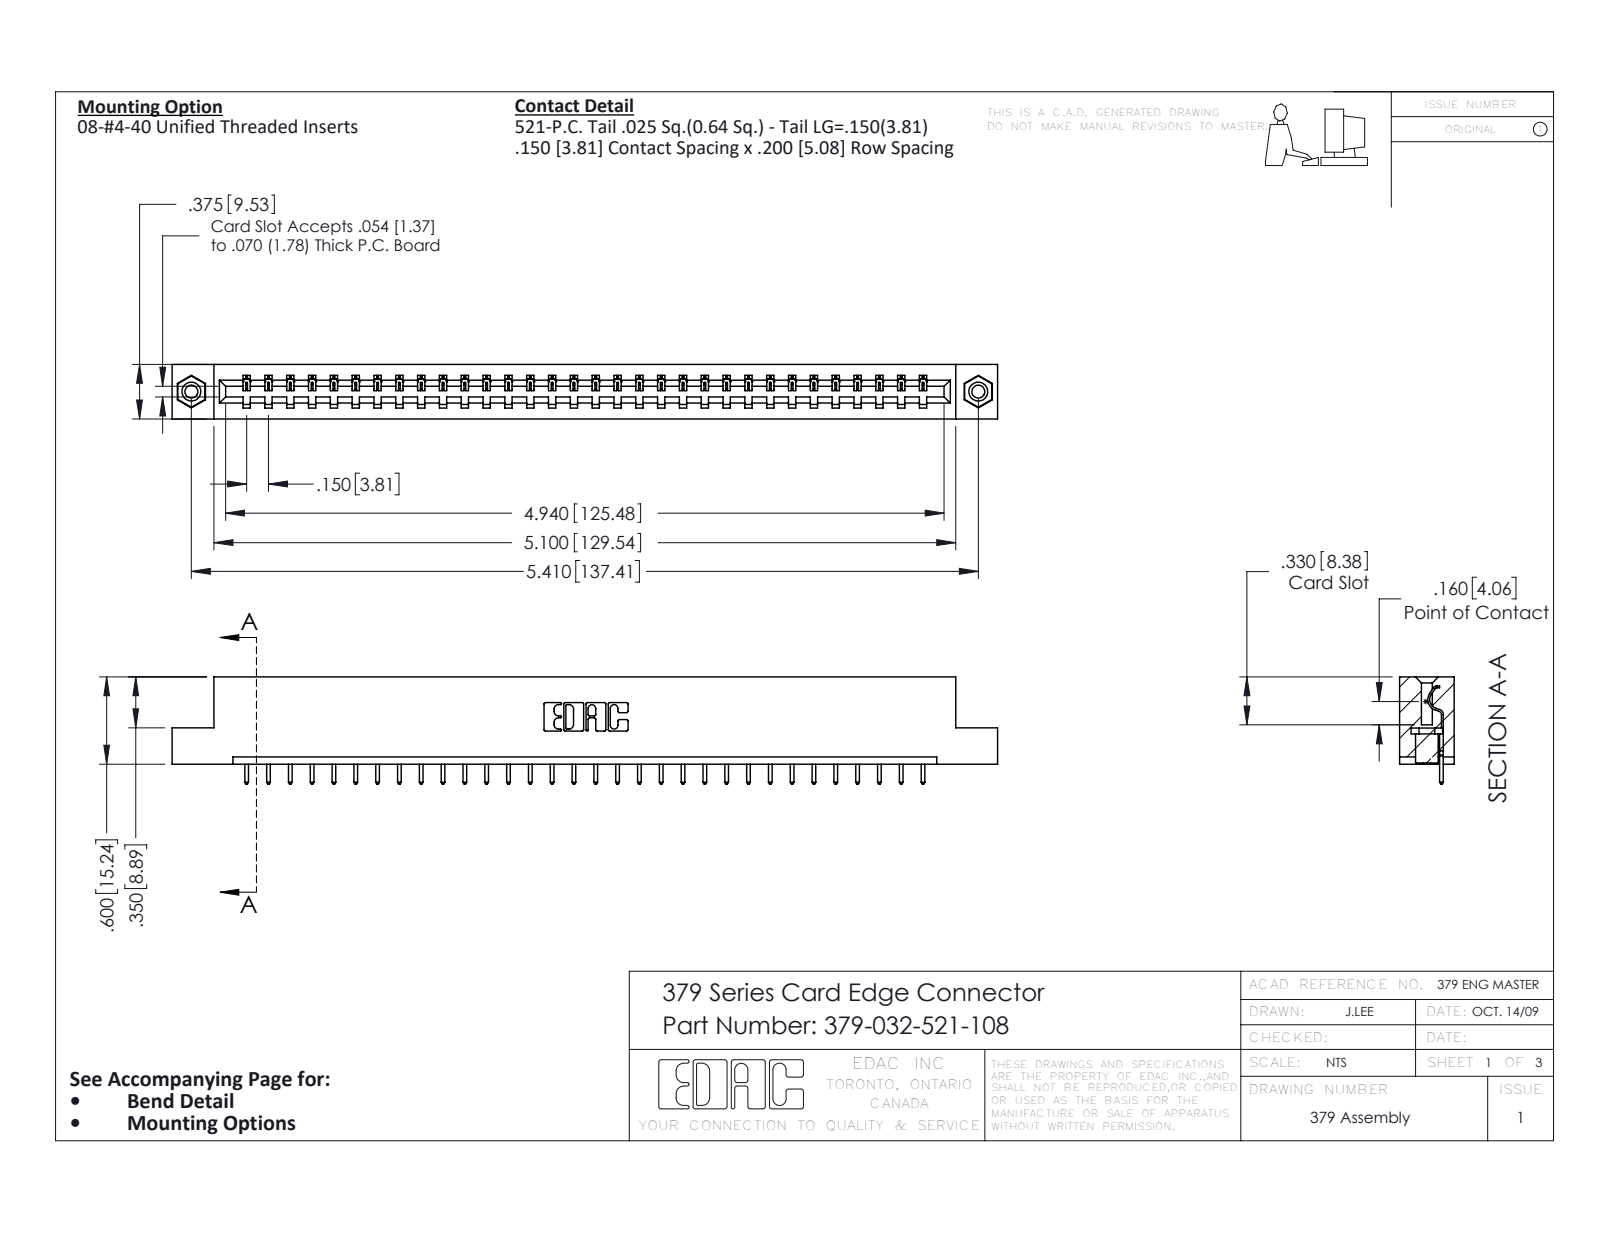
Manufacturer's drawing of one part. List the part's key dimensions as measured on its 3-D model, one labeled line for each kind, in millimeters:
Part name (STEP PRODUCT): 379-032-521-108; 345-250-001_345-250-003-102; 345-292-001_345-293-121; 379 Part_Flush - .156 Dia - TI
STEP written by: SolidWorks 2016 (CONFIG_CONTROL_DESIGN)
Units: millimetres
Bodies: 35 solids, 2030 faces (1446 planar, 568 cylindrical, 16 other)
Overall size (bounding box): 144.1 × 18.7 × 9.5
Volume: 14 900 mm³ · Surface area: 14 860 mm²
Round holes (diameter × count): ⌀2.3 ×2, ⌀3.2 ×2, ⌀4 ×2
Round bosses / shafts (diameter × count): ⌀3.9 ×2
Partial cylindrical surfaces — rounded edges, fillets, slot ends (radius × count): R0.2 ×64, R0.3 ×64, R0.3 ×22, R0.2 ×6, R0.8 ×6, R0.7 ×3, R0.4 ×1, R0.6 ×1
Main face-to-face distances: 7.6, 1.9, 9.5, 5.7, 15.2, 5.1, 7, 2.5, 0.6, 14
Hole centre spacings: 137.4
